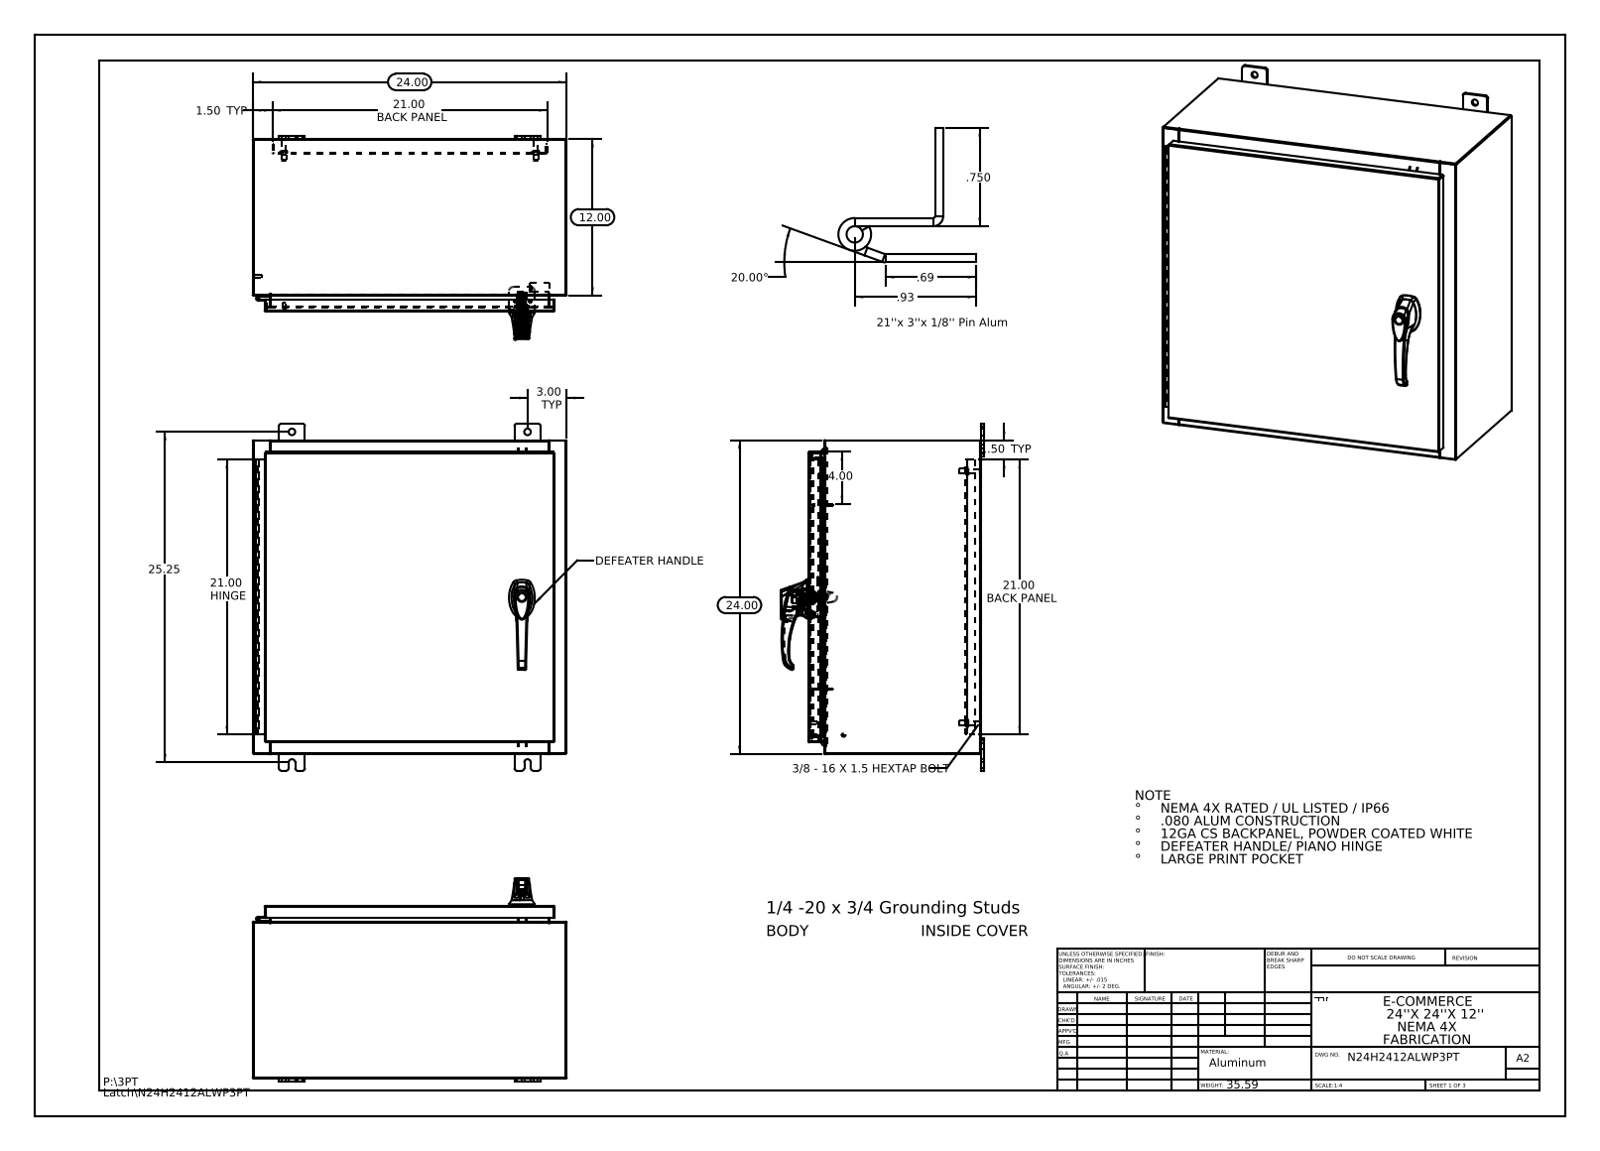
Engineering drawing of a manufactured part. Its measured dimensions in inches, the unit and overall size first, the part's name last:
Units: inches
Overall size (bounding box): 26.5 × 24 × 15.495
Round holes (diameter × count): ⌀0.5 ×8, ⌀0.25 ×4, ⌀0.138 ×3, ⌀0.161 ×3, ⌀0.079 ×2, ⌀0.203 ×2, ⌀0.313 ×2, ⌀0.437 ×2, ⌀0.125 ×1, ⌀0.125 ×1, ⌀0.197 ×1, ⌀0.276 ×1
Round bosses / shafts (diameter × count): ⌀0.625 ×4, ⌀0.375 ×4, ⌀0.33 ×4, ⌀0.157 ×4, ⌀0.14 ×4, ⌀0.315 ×3, ⌀0.236 ×3, ⌀1.181 ×1
Partial cylindrical surfaces — rounded edges, fillets, slot ends (radius × count): R0.118 ×37, R0.006 ×33, R0.19 ×24, R0.013 ×22, R0.088 ×18, R0.039 ×15, R0.028 ×12, R0.008 ×6
Main face-to-face distances: 0.075, 23.925, 13.126, 23.85, 24, 13.051, 13.201, 0.104, 1, 1.075
Hole centre spacings: 7.68, 0.295, 0.625, 0.841, 1.25, 1.313, 1.561, 1.858
Volume: 251.9 in³ · Surface area: 6 288 in²
Bodies: 37 solids, 2498 faces (883 planar, 917 cylindrical, 698 other)
Part name (STEP PRODUCT): N24H2412ALWP3PT Top; N24H2412ALWP3PT Mounting Studs; 012103_012102; N24H2412ALWP3PT Hinge Enclosure Side2 (+8 more)
STEP written by: SolidWorks 2013 (CONFIG_CONTROL_DESIGN)
